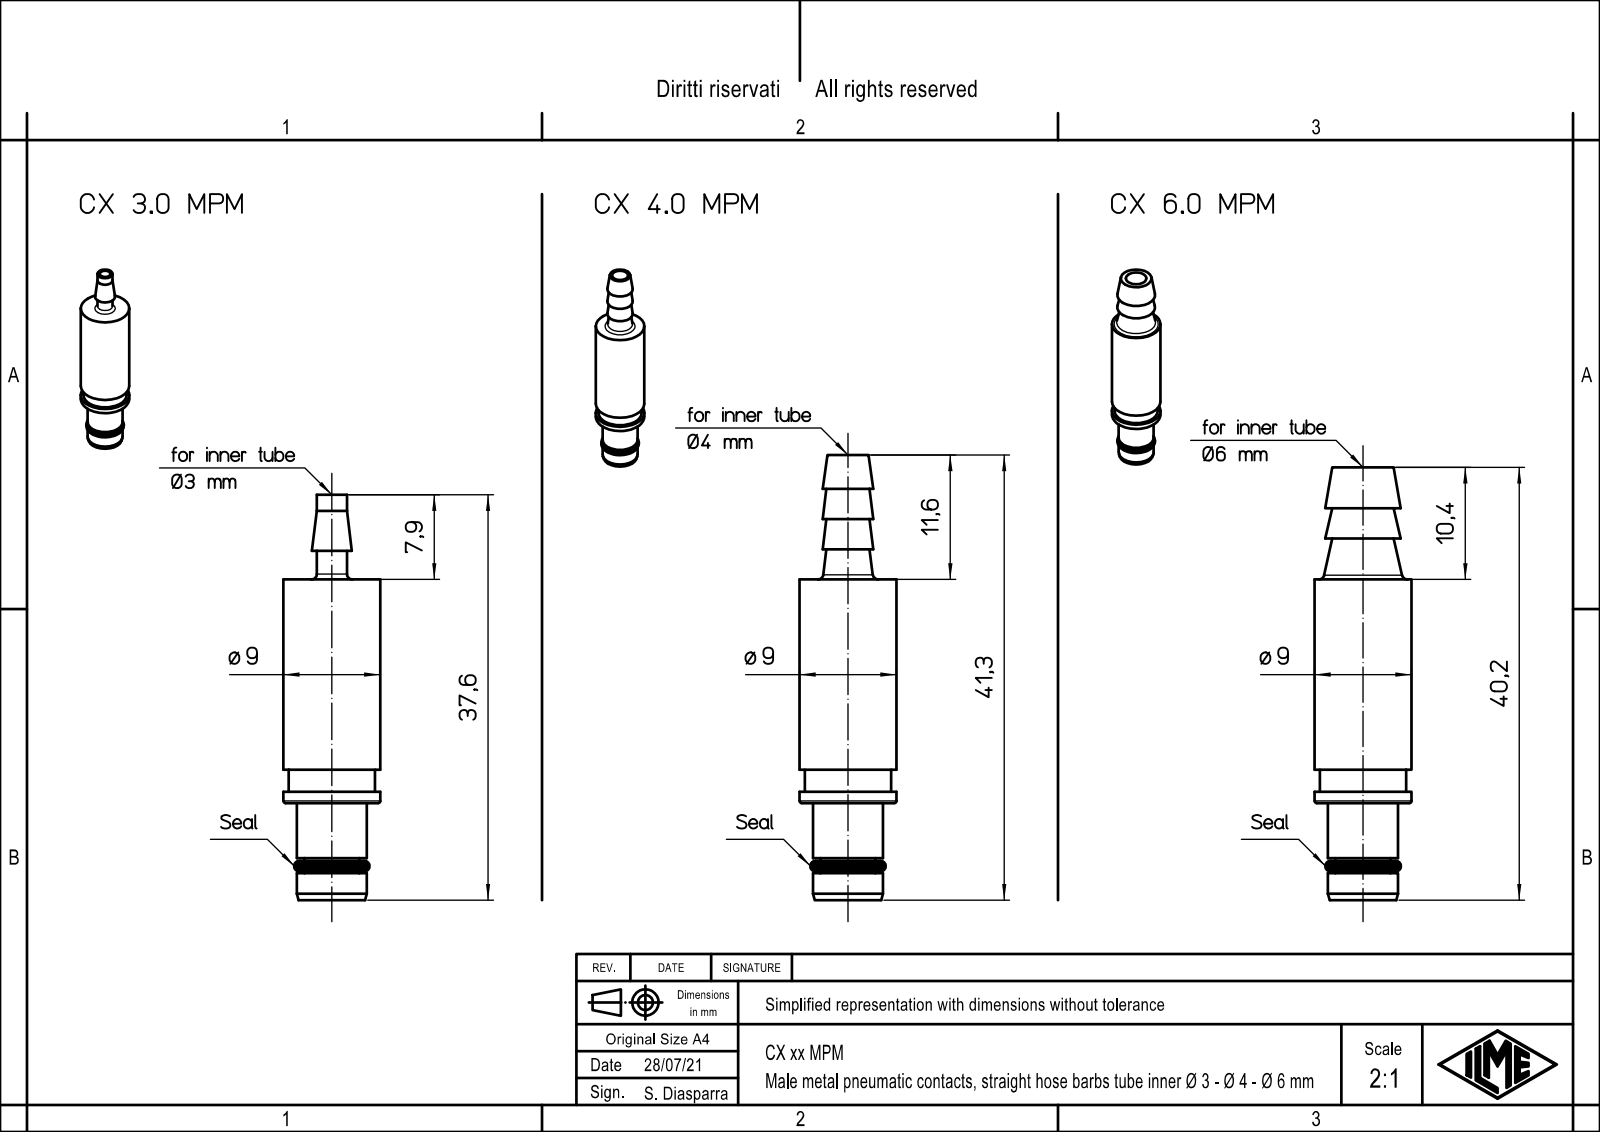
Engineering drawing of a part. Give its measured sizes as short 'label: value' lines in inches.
name: CX_4.0_MPM
written by: Creo Elements/Direct Modeling 20.1B 02-Apr-2019 (C) Parametric Technology GmbH (AUTOMOTIVE_DESIGN)
unit: in
bodies: 1 solid, 49 faces (11 planar, 18 cylindrical, 20 other)
size: 1.626 × 0.354 × 0.354
volume: 0.082 in³; area: 2.457 in²
holes: 1× ⌀0.118, 1× ⌀0.15
bosses: 1× ⌀0.354, 1× ⌀0.315, 1× ⌀0.256, 1× ⌀0.201
face distances: 0.817, 0.354, 1.171, 0.11, 0.396, 0.041, 0.776, 0.476, 0.122, 0.081
